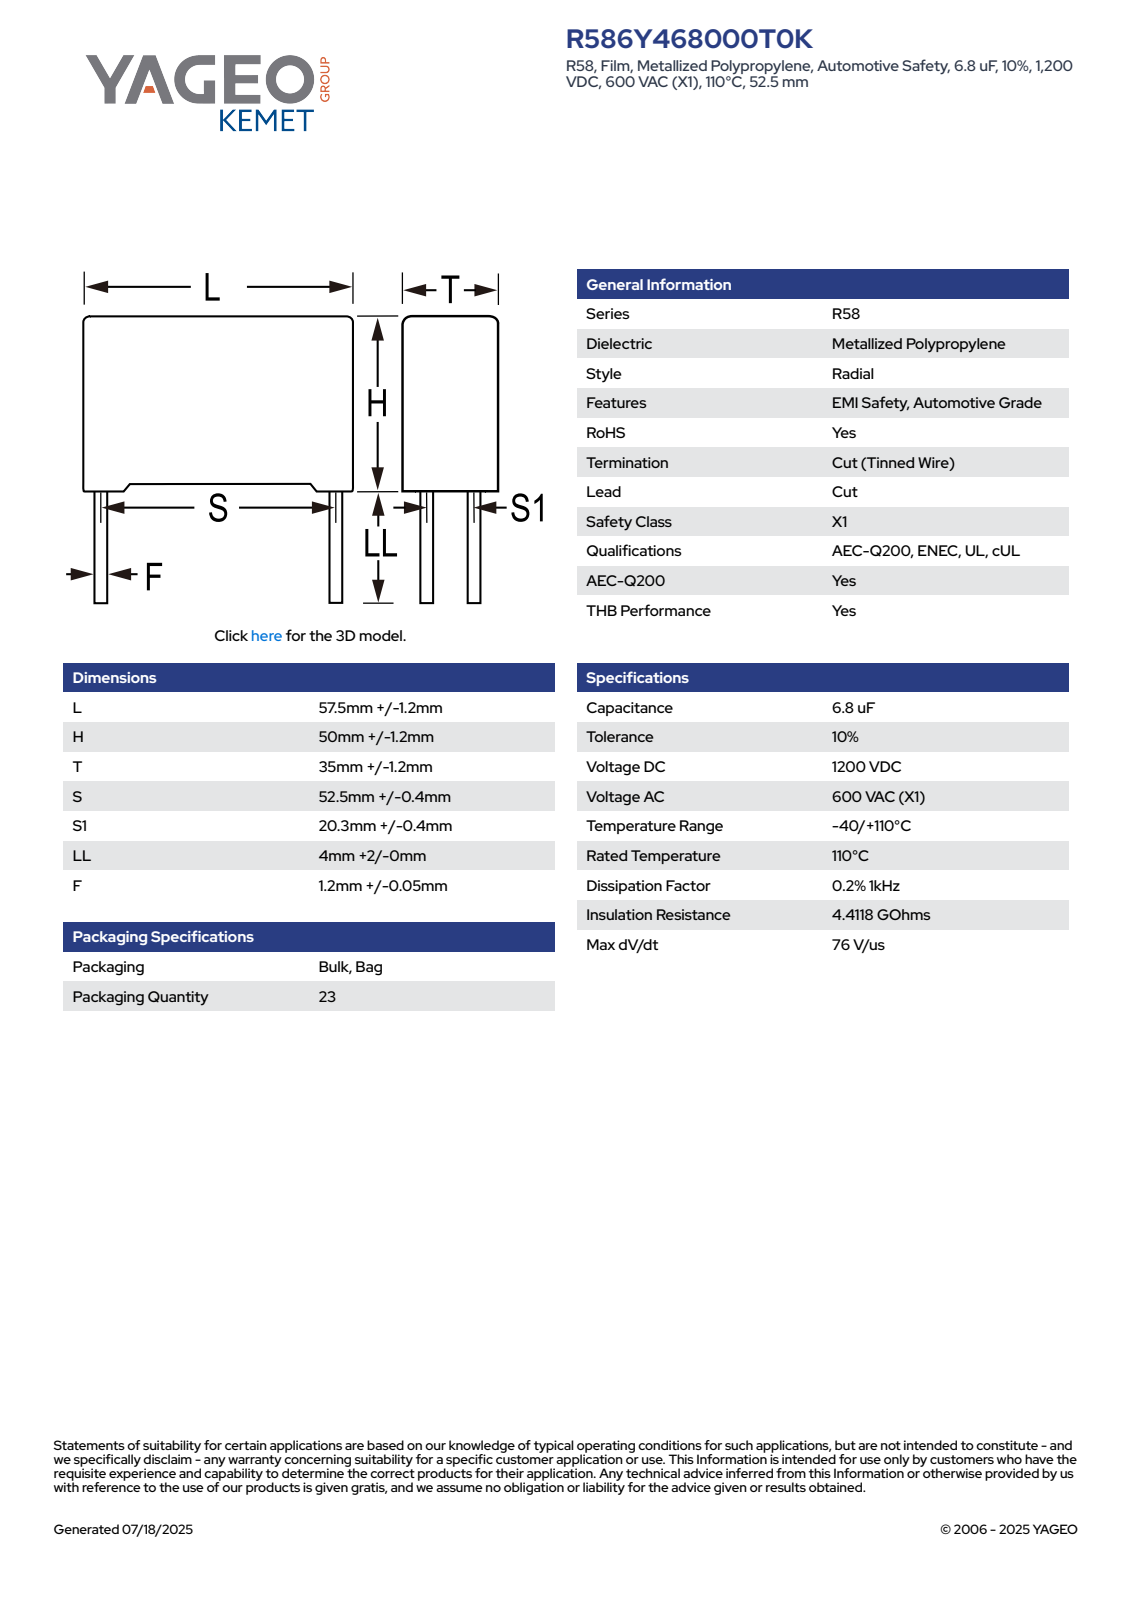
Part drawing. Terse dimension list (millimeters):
name: CFP_RB4_57.5X50X35_L58.7H51.2T36.2S52.5S120.3LL6F1.25
written by: SolidWorks 2021 (AUTOMOTIVE_DESIGN)
unit: mm
bodies: 4 solids, 87 faces (79 planar, 8 cylindrical, 0 other)
size: 58.7 × 57.2 × 36.2
volume: 105 955 mm³; area: 14 317 mm²
bosses: 4× ⌀1.25
face distances: 36.2, 49.69, 58.7, 1.51, 51.2, 2.23, 56.47, 54.24, 33.97, 31.74
